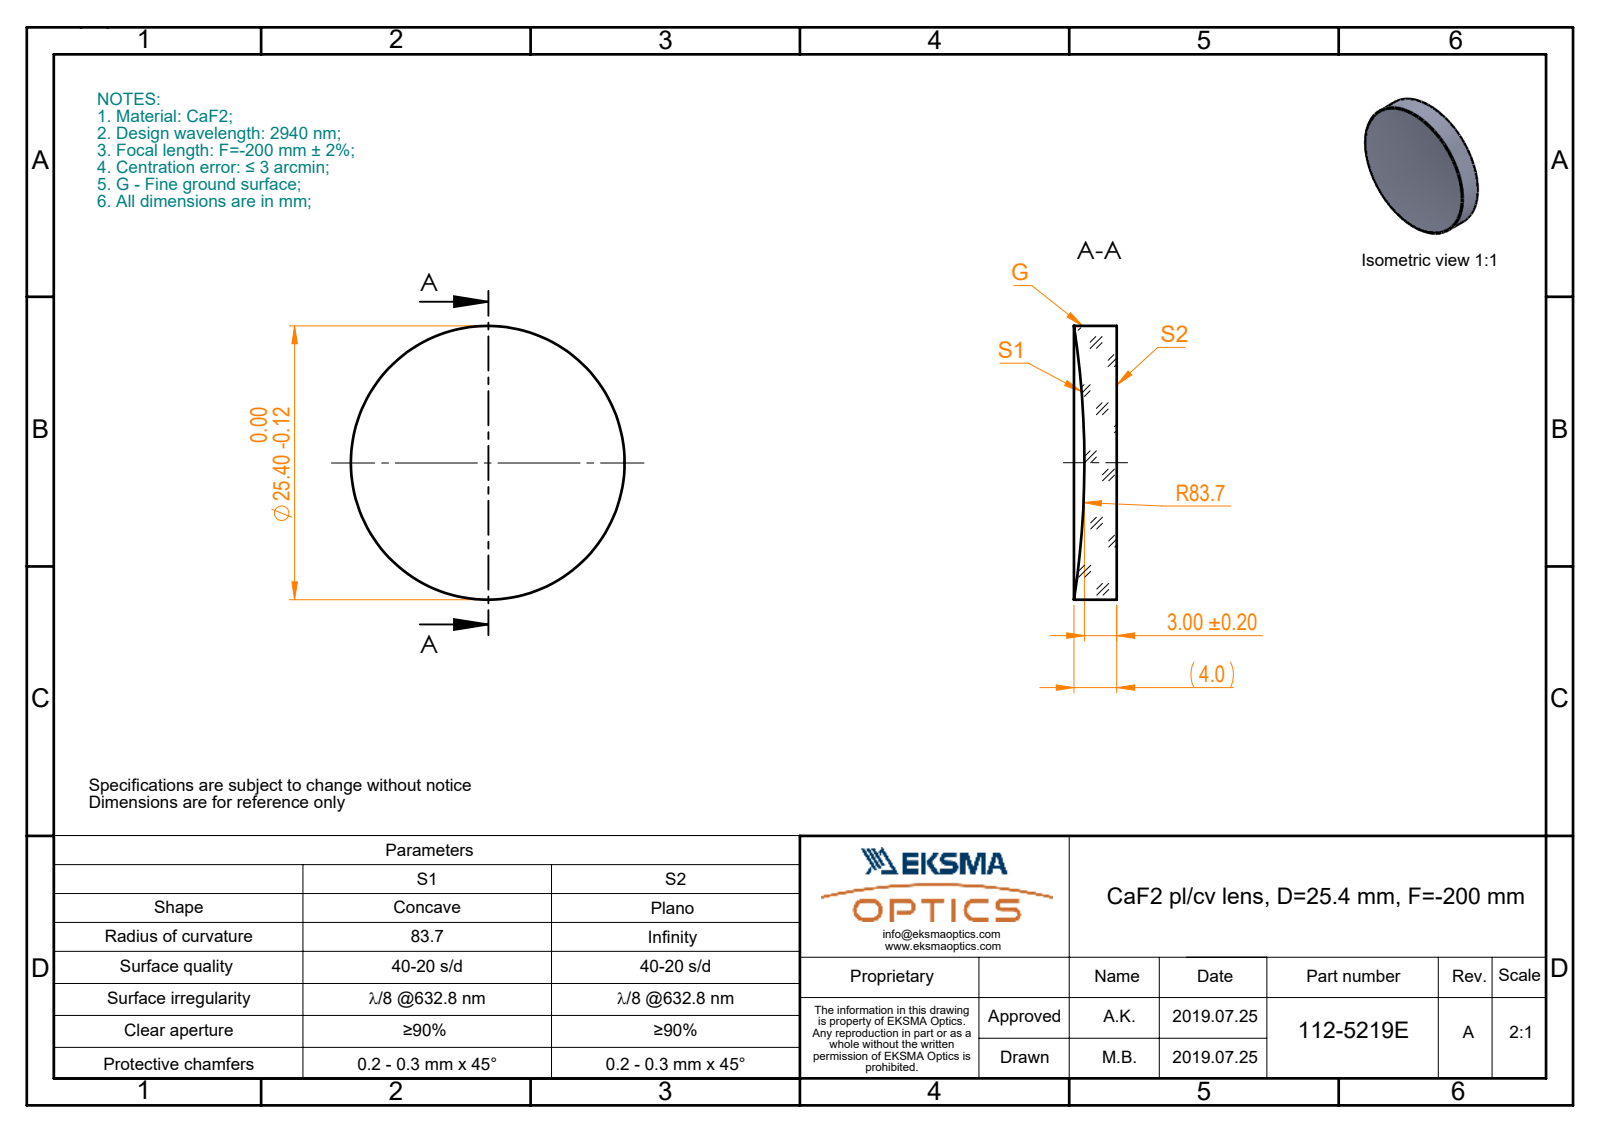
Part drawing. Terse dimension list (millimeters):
name: 112-5219E CaF2 pl-cv 12.7 F-200
written by: SolidWorks 2017 (CONFIG_CONTROL_DESIGN)
unit: mm
bodies: 1 solid, 5 faces (1 planar, 2 cylindrical, 2 other)
size: 25.4 × 25.4 × 3.97
volume: 1 765 mm³; area: 1 333 mm²
bosses: 1× ⌀25.4
